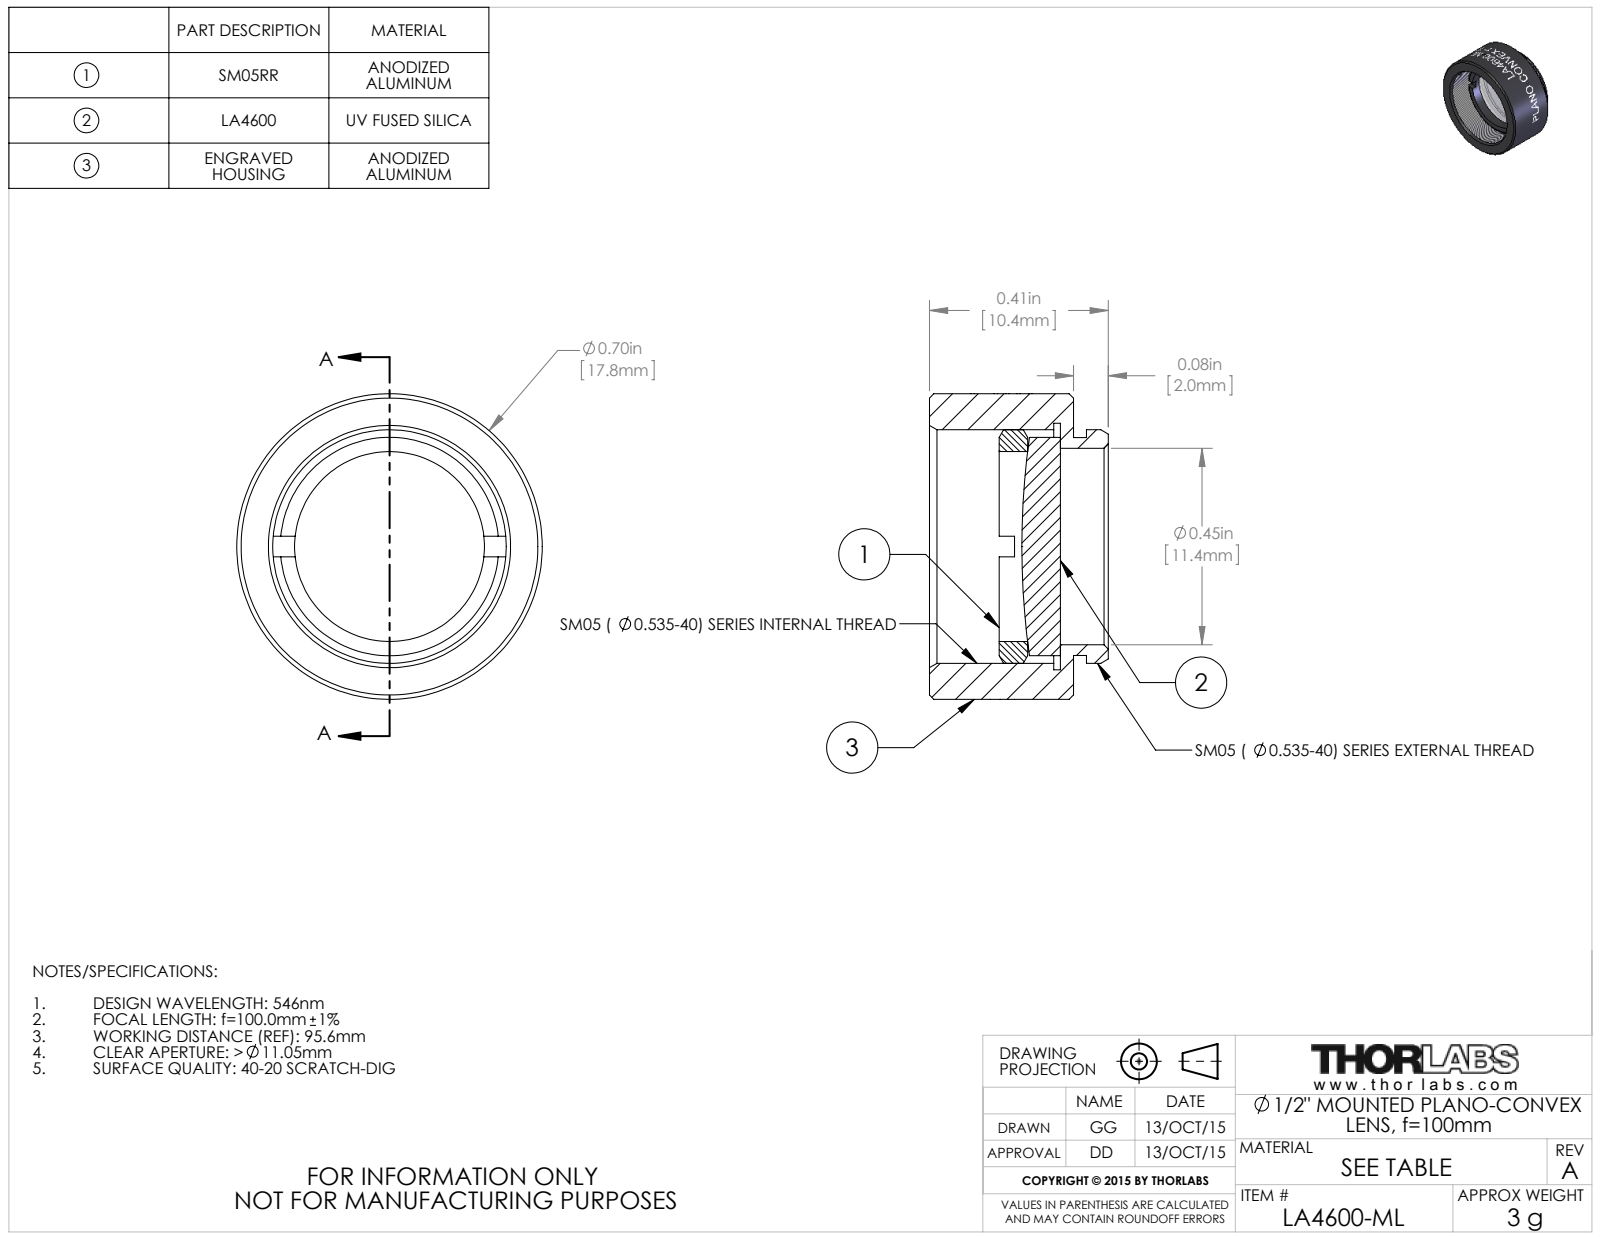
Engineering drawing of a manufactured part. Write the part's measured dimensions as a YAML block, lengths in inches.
part_name: "TTN039324-E0W"
step_written_by: "SolidWorks 2014 (CONFIG_CONTROL_DESIGN)"
units: inches
bodies: {solids: 3, faces: 110, planar: 16, cylindrical: 77, other: 17}
overall_size: [0.7, 0.7, 0.41]
volume: 0.078
surface_area: 2.852
round_holes:
  - {diameter: 0.435, count: 1}
  - {diameter: 0.45, count: 1}
  - {diameter: 0.535, count: 1}
  - {diameter: 0.565, count: 1}
round_bosses_or_shafts:
  - {diameter: 0.7, count: 1}
  - {diameter: 0.535, count: 1}
  - {diameter: 0.5, count: 1}
  - {diameter: 0.499, count: 1}
face_to_face_distances: [0.03, 0.33, 0.3, 0.075, 0.06, 0.105, 0.225, 0.17, 0.14, 0.065]
